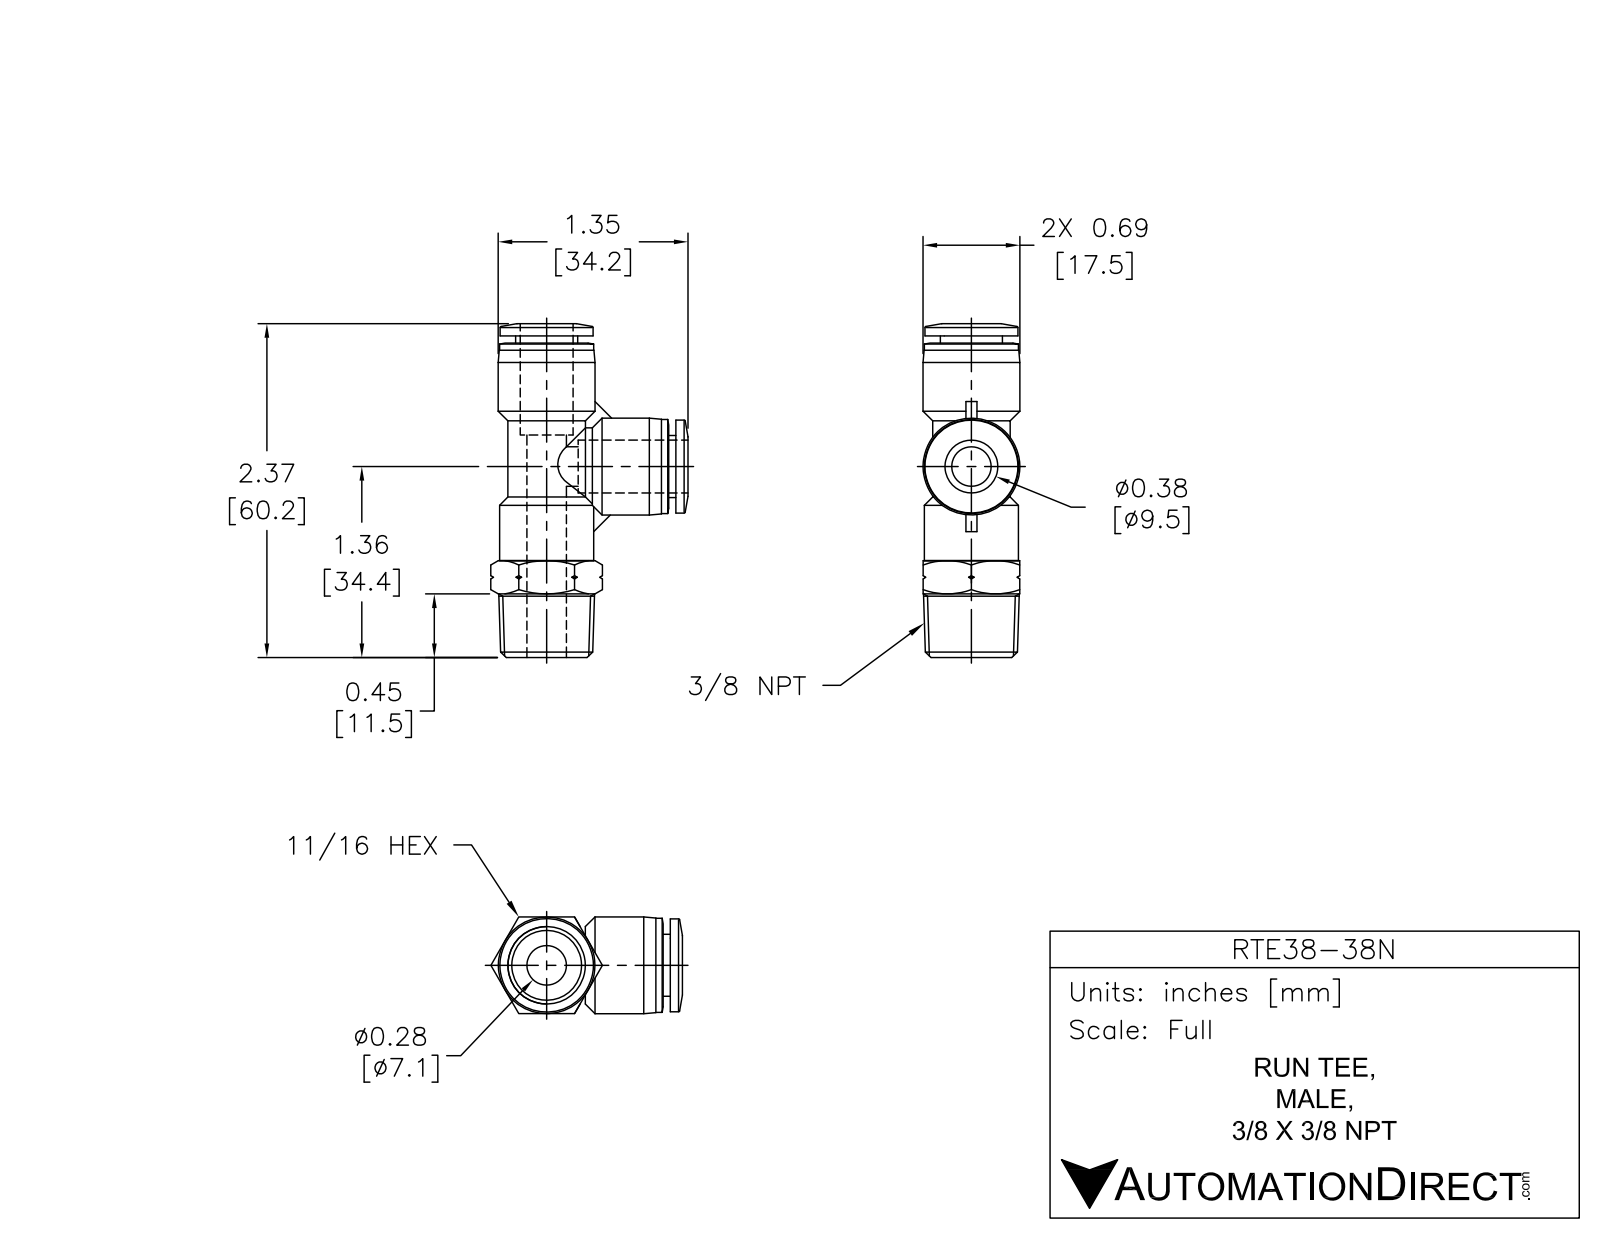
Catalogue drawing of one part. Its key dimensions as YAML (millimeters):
part_name: "MRT38-38N"
step_written_by: "SolidWorks 2015 (AUTOMOTIVE_DESIGN)"
units: millimeters
bodies: {solids: 1, faces: 117, planar: 23, cylindrical: 30, other: 64}
overall_size: [60.3, 35.9, 17.5]
volume: 11700
surface_area: 7303
round_holes:
  - {diameter: 8, count: 2}
  - {diameter: 9.8, count: 2}
round_bosses_or_shafts:
  - {diameter: 17.5, count: 2}
  - {diameter: 17, count: 2}
  - {diameter: 16.8, count: 2}
  - {diameter: 14, count: 2}
  - {diameter: 11.2, count: 2}
face_to_face_distances: [17.4, 1.3, 58.1, 56.8, 16.6, 17.9, 7.7, 9.7, 40.2, 2]
